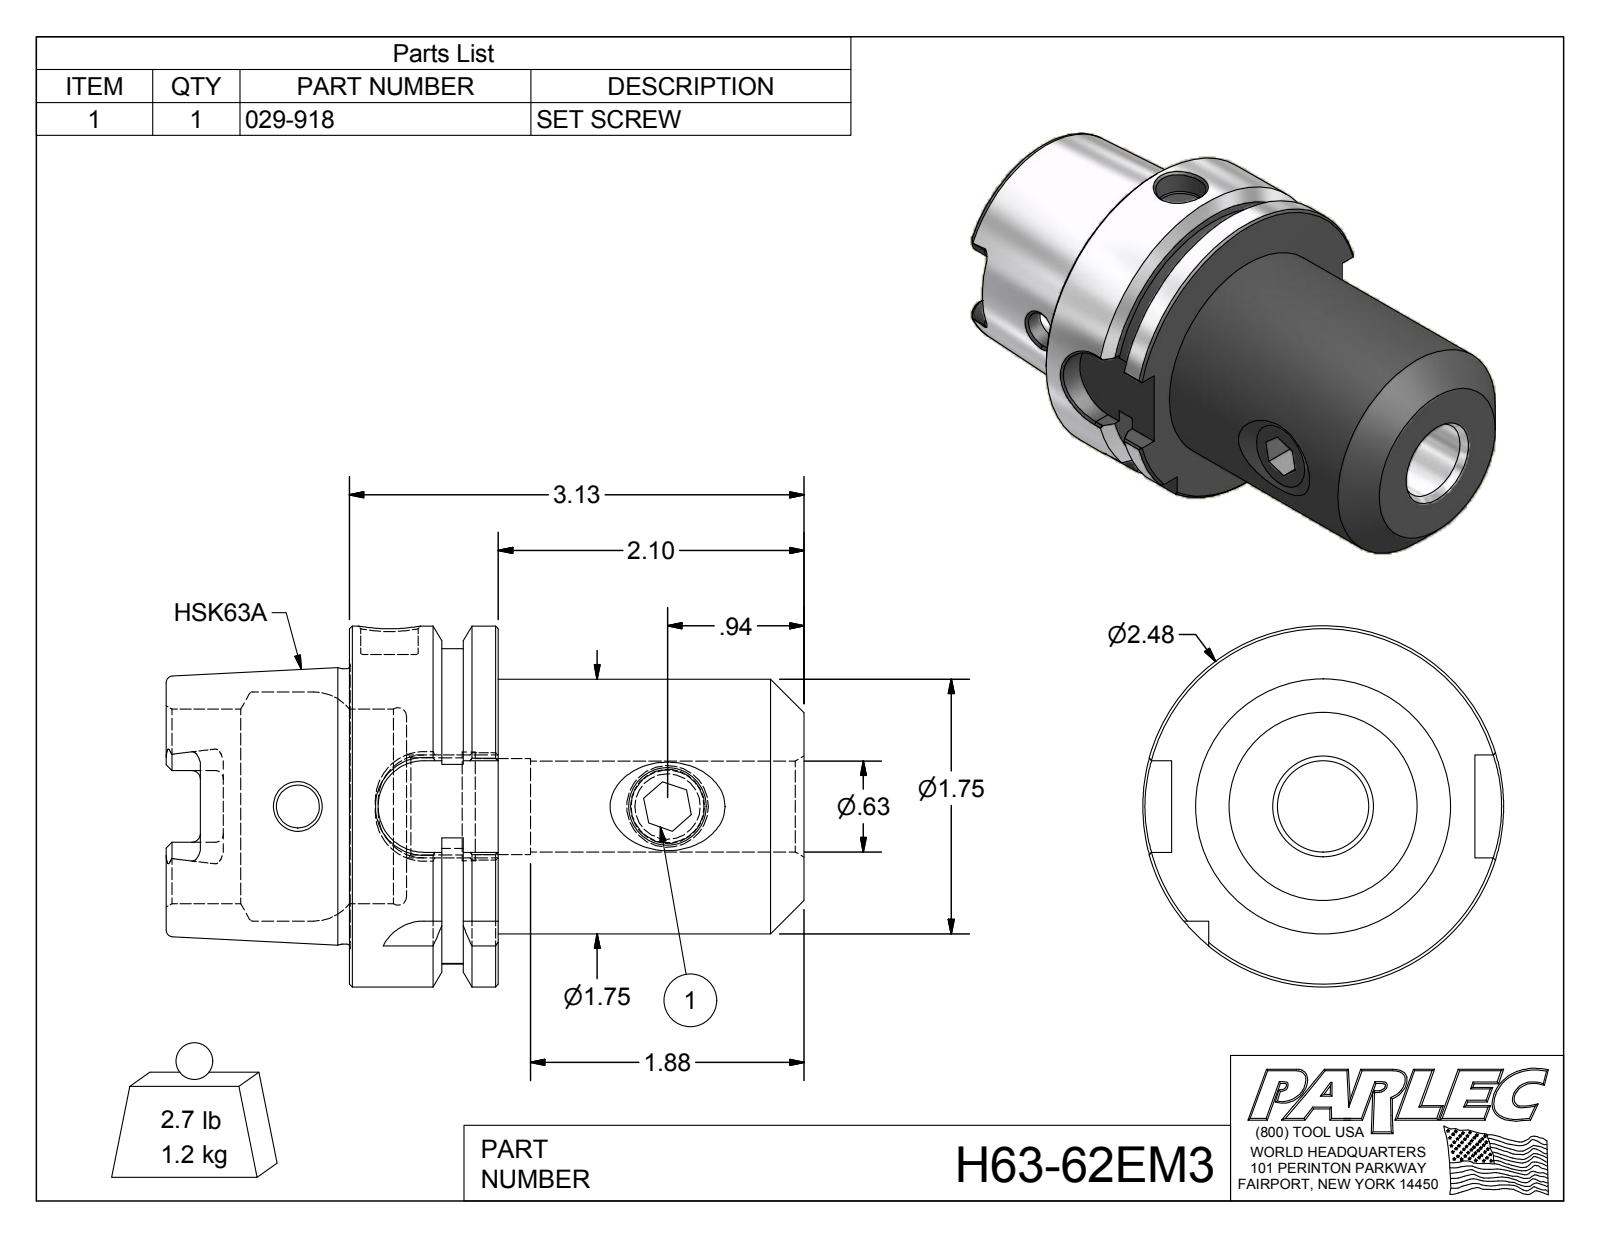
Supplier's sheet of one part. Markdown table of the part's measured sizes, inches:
| quantity | value |
| --- | --- |
| part name | H63-62EM3; H63-62EM3-1; 029-918 |
| STEP written by | Autodesk Inventor 2012 (AUTOMOTIVE_DESIGN) |
| units | inches |
| bodies | 2 solids, 146 faces (61 planar, 36 cylindrical, 49 other) |
| overall size | 4.385 × 2.48 × 2.48 |
| volume | 9.128 in³ |
| surface area | 51.49 in² |
| round holes (diameter × count) | 0.295 × 1, 0.394 × 1, 0.502 × 1, 0.625 × 1, 0.66 × 1, 0.666 × 1, 0.749 × 1, 1.339 × 1, 1.575 × 1 |
| round bosses / shafts (diameter × count) | 2.48 × 1, 1.891 × 1, 1.75 × 1, 0.563 × 1 |
| partial cylindrical surfaces (radius × count) | 0.059 × 6, 0.113 × 4, 0.315 × 4, 1.083 × 1 |
| main face-to-face distances | 1.024, 3.125, 2.102, 0.394, 0.63, 2.731, 1.26, 0.241, 1.654, 2.283 |
| hole center spacings | 2.541 |
